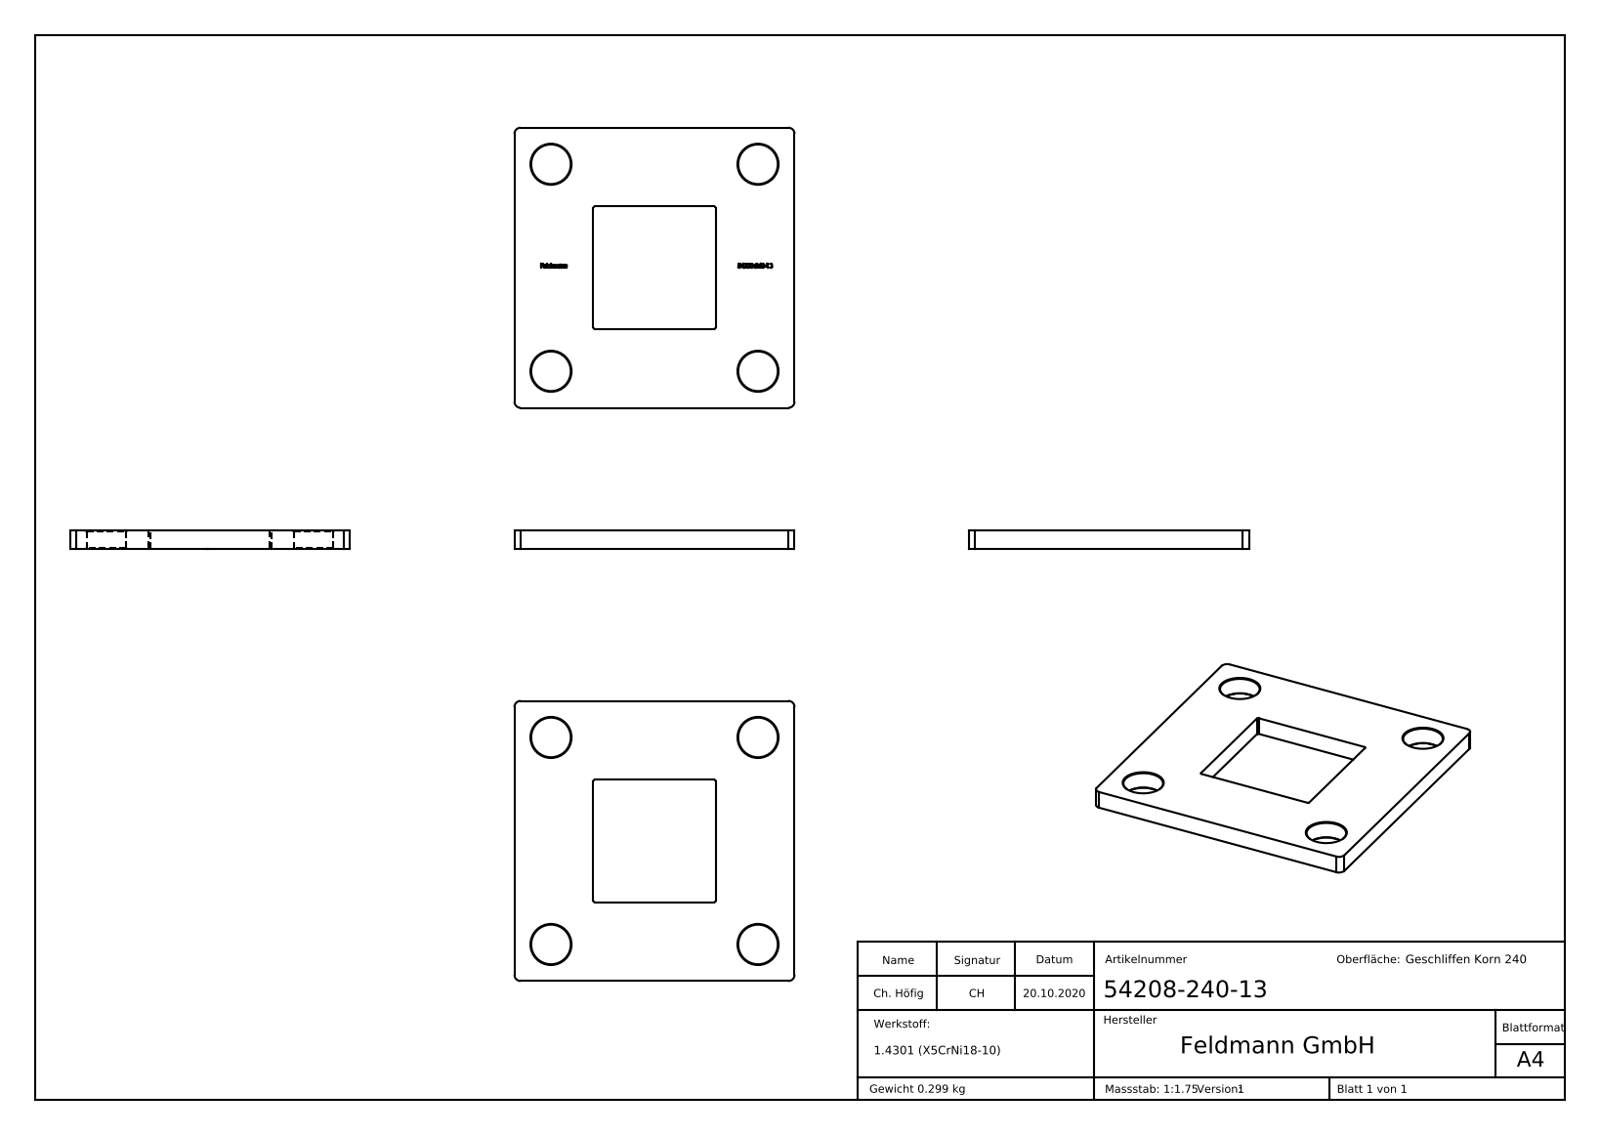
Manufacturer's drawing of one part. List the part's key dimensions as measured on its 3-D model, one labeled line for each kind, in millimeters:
Part name (STEP PRODUCT): 54208-240-13
STEP written by: SolidWorks 2018 (CONFIG_CONTROL_DESIGN)
Units: millimetres
Bodies: 1 solid, 303 faces (154 planar, 16 cylindrical, 133 other)
Overall size (bounding box): 92 × 92 × 6
Volume: 37 872 mm³ · Surface area: 16 719 mm²
Round holes (diameter × count): ⌀13 ×4
Partial cylindrical surfaces — rounded edges, fillets, slot ends (radius × count): R0.5 ×4, R2 ×4
Main face-to-face distances: 6, 92, 25.9, 66.1, 40.2, 5.9, 46, 20.1, 0.44, 0.88
Hole centre spacings: 68, 96.17
